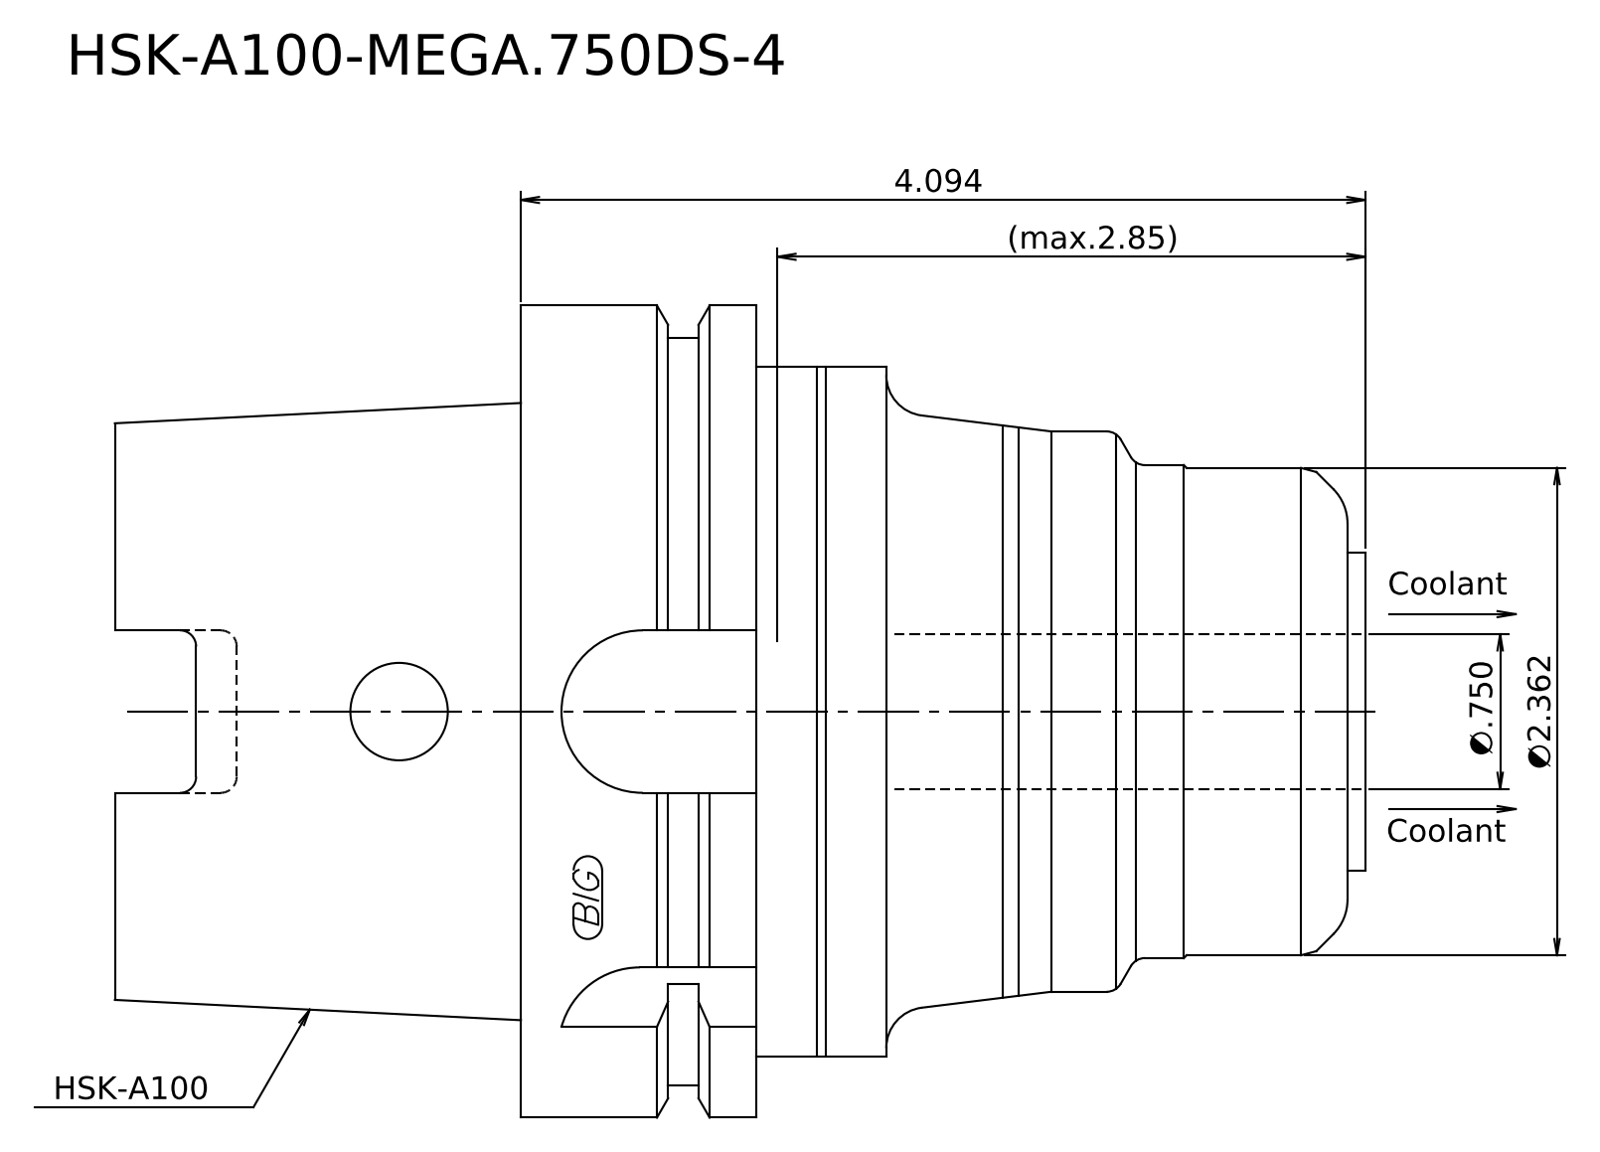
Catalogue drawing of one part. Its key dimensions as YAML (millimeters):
step_written_by: "Kubotek KeyCreator 2011 V10.0.2 (22737) (automotive_design)"
units: millimeters
bodies: {solids: 1, faces: 25, planar: 8, cylindrical: 8, other: 9}
overall_size: [154, 100, 100]
volume: 722261
surface_area: 51770
round_bosses_or_shafts:
  - {diameter: 100, count: 1}
  - {diameter: 92, count: 1}
  - {diameter: 85, count: 1}
  - {diameter: 69, count: 1}
  - {diameter: 60.7, count: 1}
  - {diameter: 60, count: 1}
  - {diameter: 39.25, count: 1}
face_to_face_distances: [50, 29, 79, 75, 104, 154, 2.2, 72.8, 101.8, 151.8]
